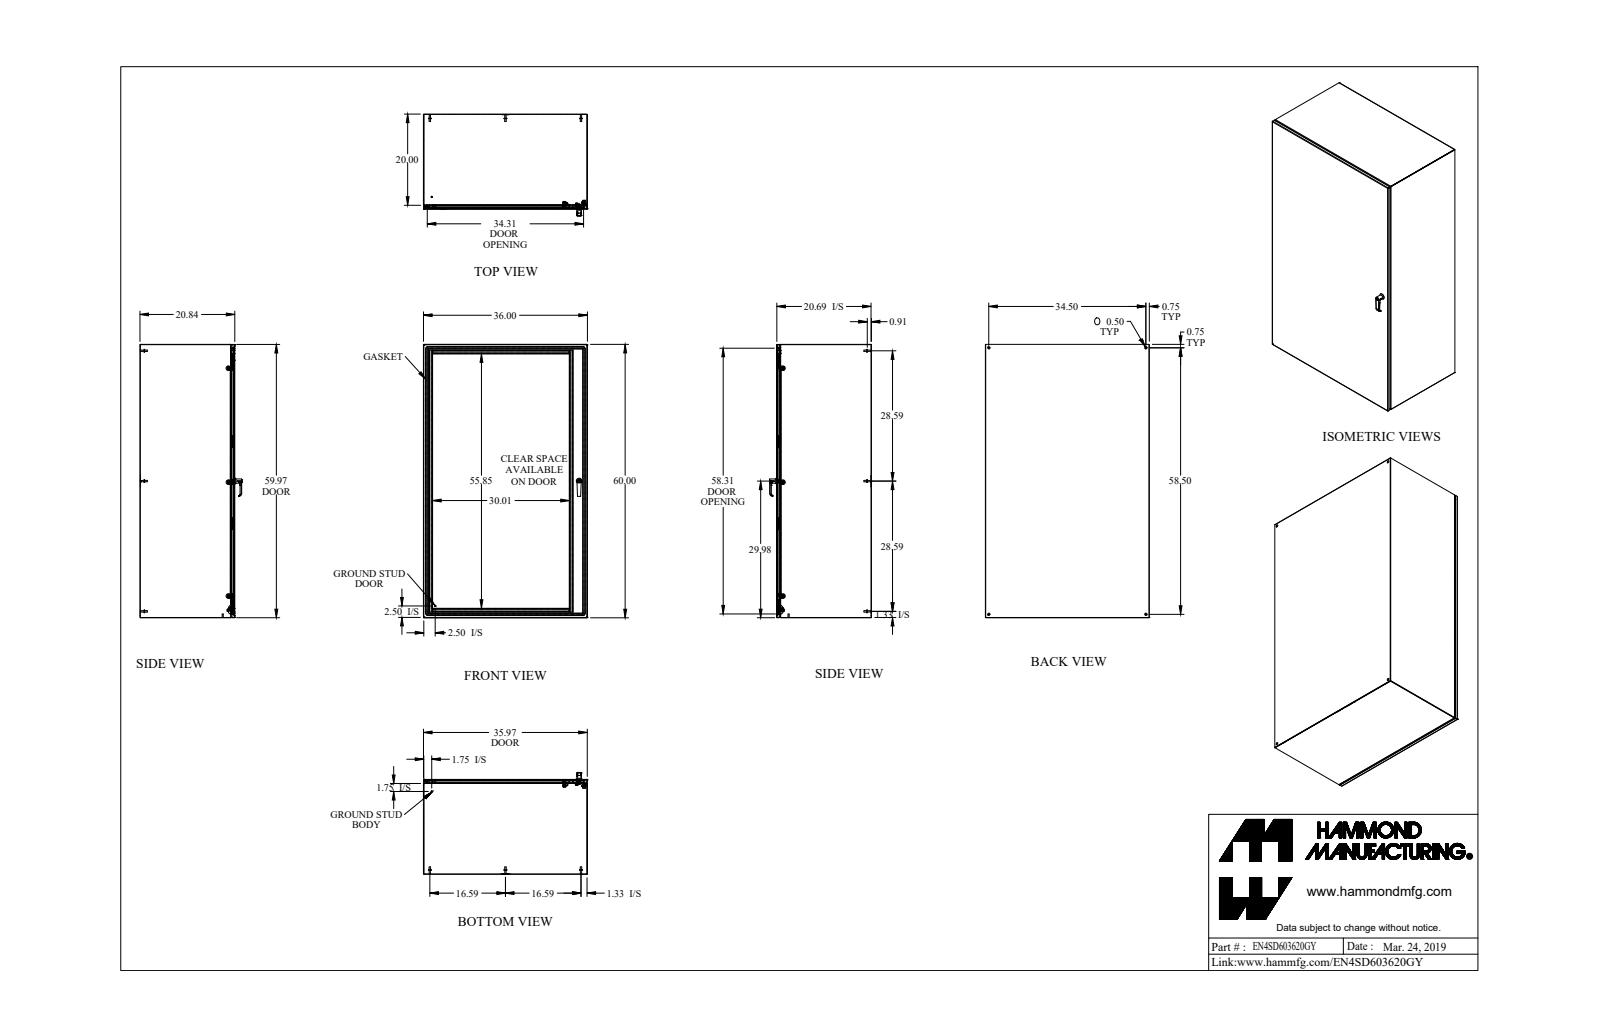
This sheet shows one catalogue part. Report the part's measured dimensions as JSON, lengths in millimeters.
{"part_name": "EN4SD603620GY", "step_written_by": "SolidWorks 2018 (AUTOMOTIVE_DESIGN)", "units": "millimeters", "bodies": {"solids": 64, "faces": 1715, "planar": 761, "cylindrical": 632, "other": 322}, "overall_size": [1524, 914.4, 568.1], "volume_mm3": 10850000, "surface_area_mm2": 12030000, "round_holes": [[4.5, 6], [5, 4], [12.7, 4], [6.4, 3], [6.7, 3], [10.5, 3], [6.5, 2], [8, 2], [10, 2], [4.4, 1], [6.1, 1], [6.1, 1]], "round_bosses_or_shafts": [[8, 8], [6.9, 8], [6.4, 7], [15.9, 6], [4, 6], [9.5, 5], [25.4, 3], [15.9, 3]], "partial_cylinders_radius": [[1.1, 24], [1.6, 21], [0.9, 17], [2.7, 17], [0.8, 15], [2.4, 10], [0.4, 9], [0.2, 8]], "face_to_face_distances": [1.8, 527.4, 912.6, 525.6, 529.3, 1522.2, 910.7, 914.4, 1520.3, 1524], "hole_center_spacings": [111.7, 634.5, 635, 635.5, 855.9, 876.3, 1270, 1377.8]}
